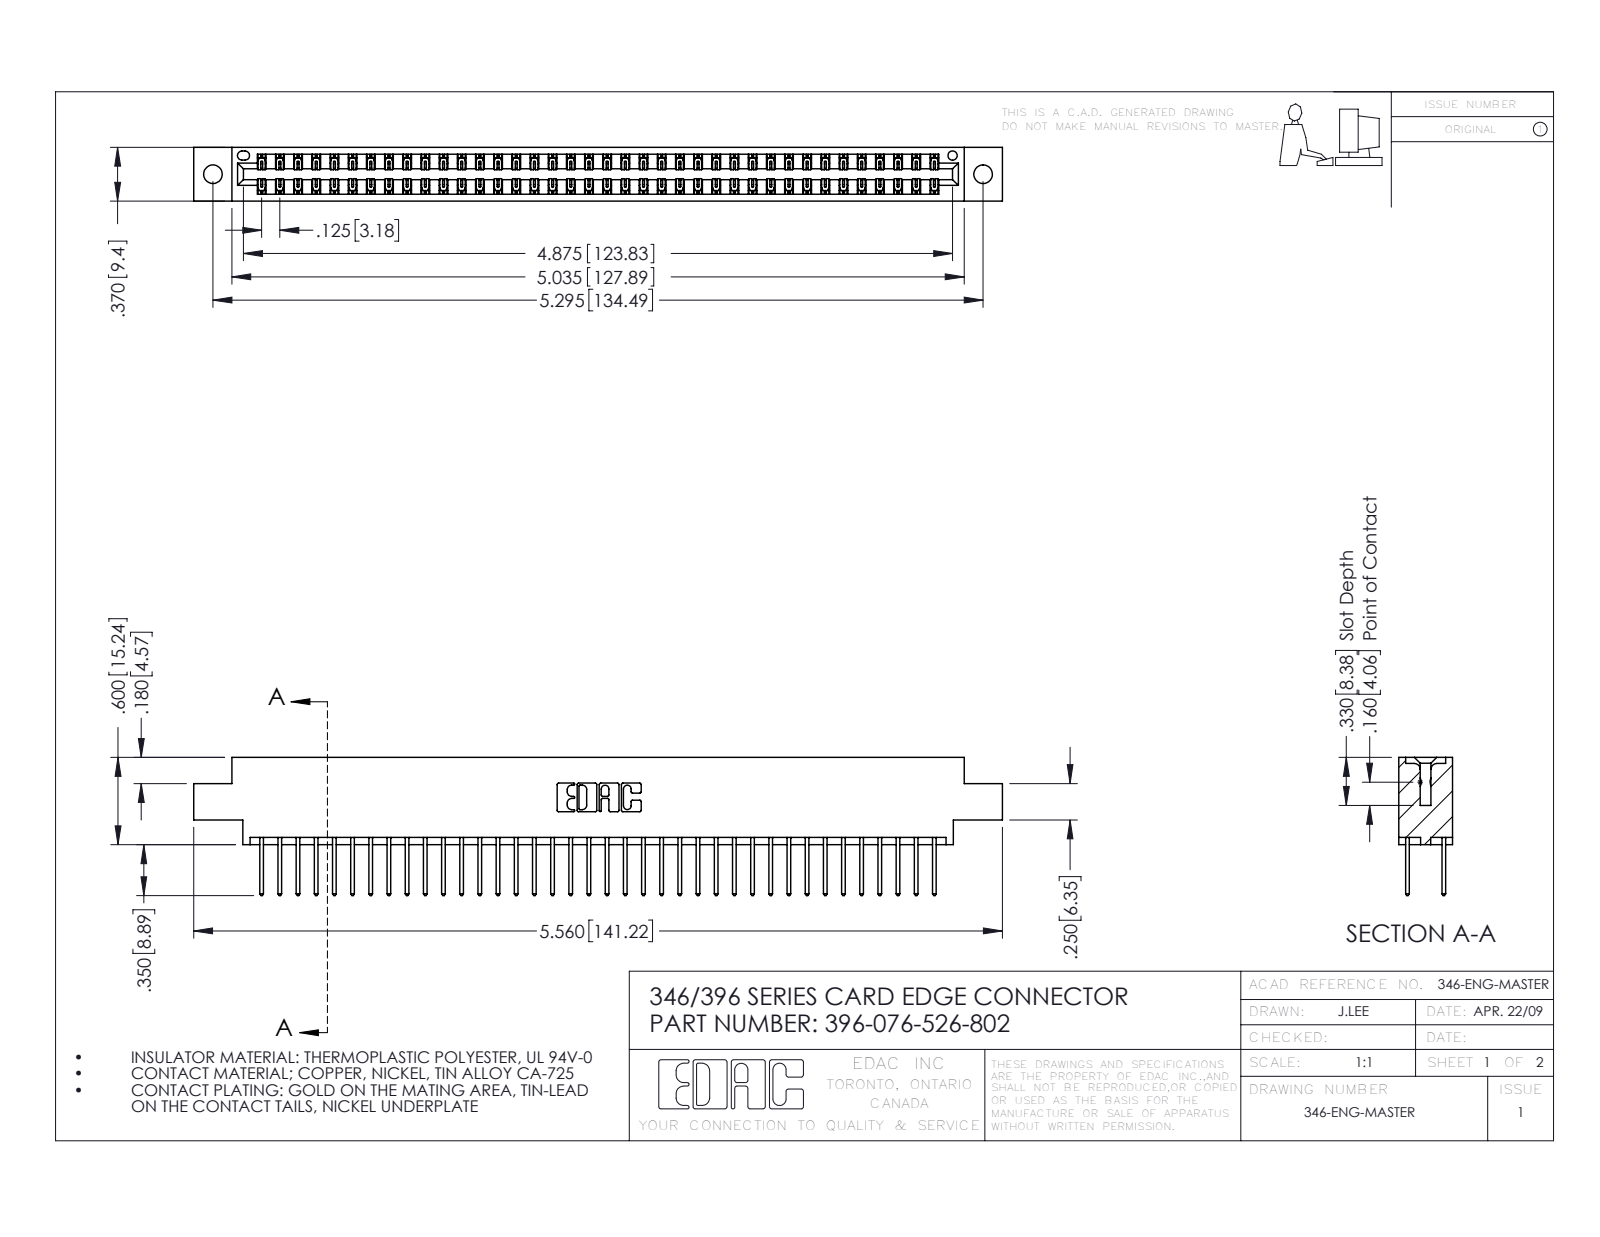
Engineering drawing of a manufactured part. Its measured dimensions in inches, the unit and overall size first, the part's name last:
Units: inches
Overall size (bounding box): 5.56 × 0.95 × 0.37
Round holes (diameter × count): ⌀0.128 ×2, ⌀0.064 ×1
Partial cylindrical surfaces — rounded edges, fillets, slot ends (radius × count): R0.006 ×114, R0.01 ×76, R0.01 ×22, R0.007 ×6, R0.031 ×6, R0.026 ×3, R0.014 ×2, R0.022 ×2
Main face-to-face distances: 0.048, 0.322, 0.25, 0.37, 0.072, 0.298, 0.025, 0.275, 0.148, 0.222
Hole centre spacings: 0.246, 5.086, 5.295
Volume: 0.834 in³ · Surface area: 29.76 in²
Bodies: 77 solids, 4078 faces (2740 planar, 1338 cylindrical, 0 other)
Part name (STEP PRODUCT): 396-076-526-802; 346 Part_0.170 Offset - 0.128 Dia; 345-292-001_345-293-126
STEP written by: SolidWorks 2016 (CONFIG_CONTROL_DESIGN)
